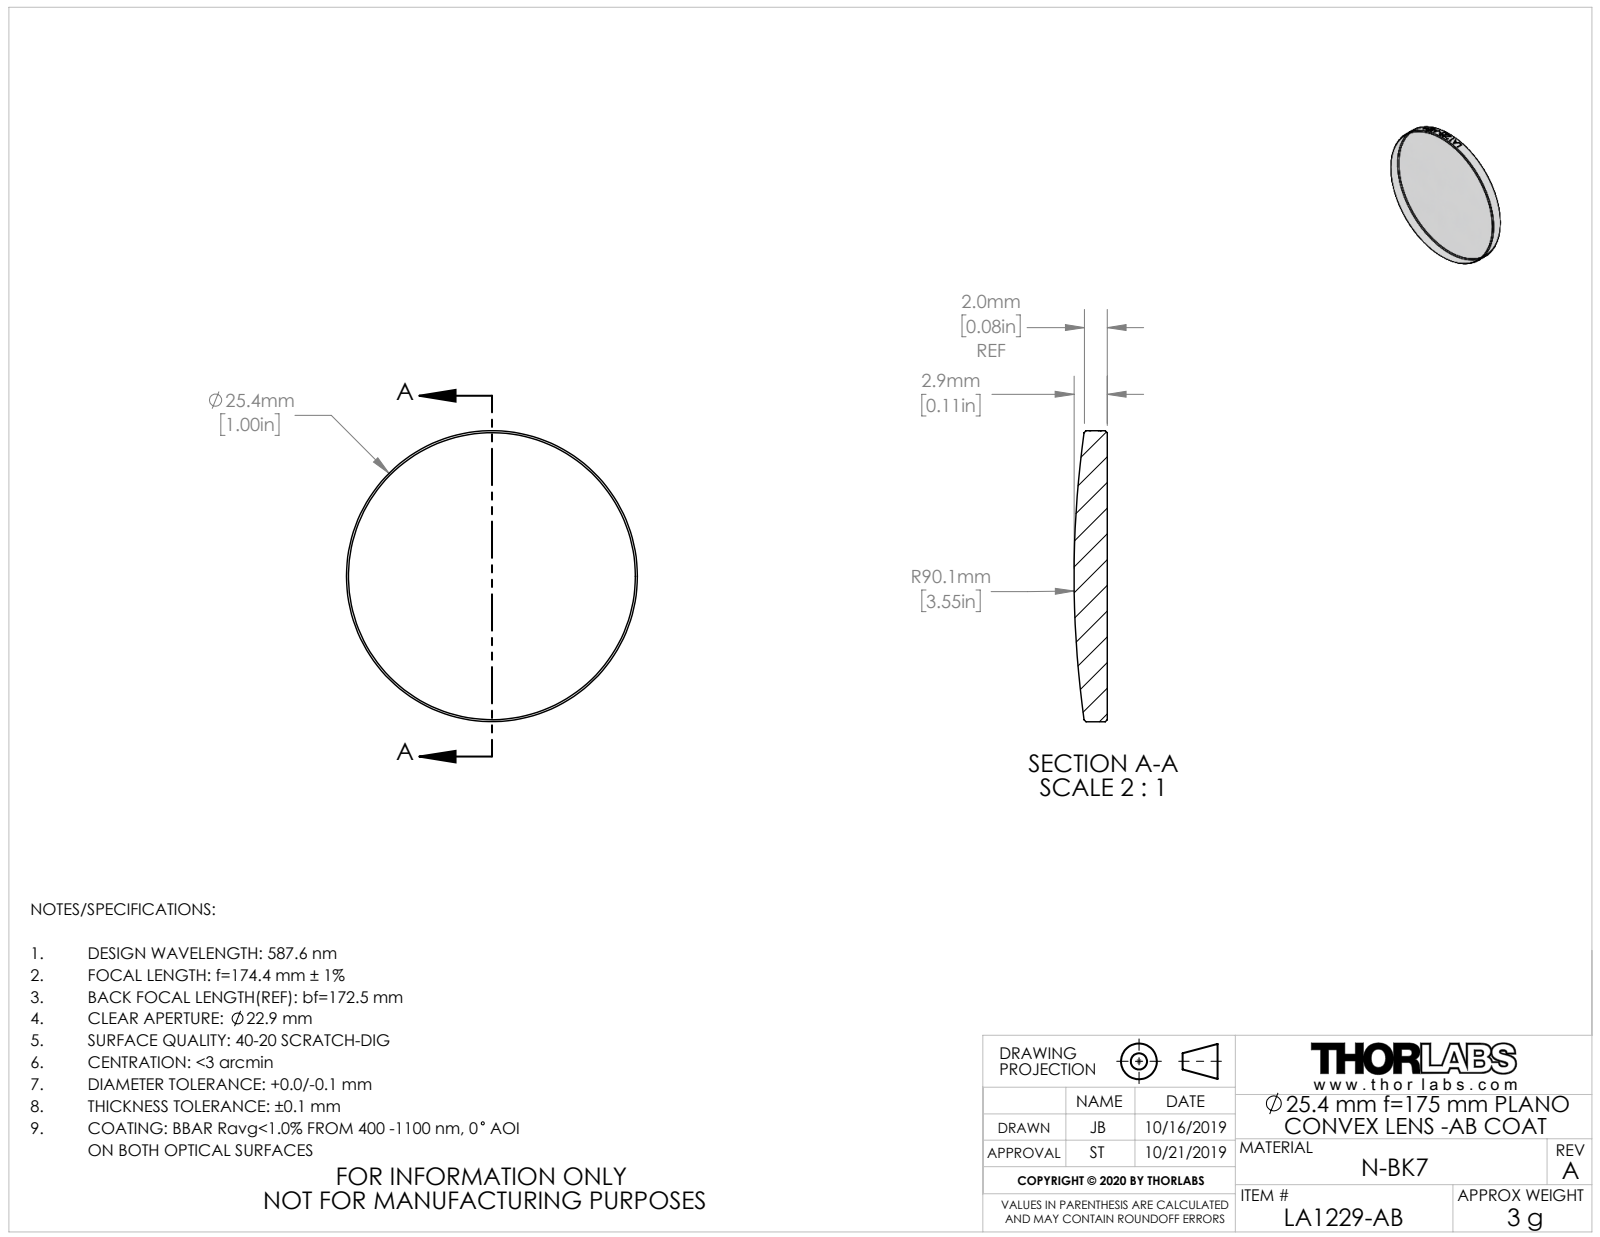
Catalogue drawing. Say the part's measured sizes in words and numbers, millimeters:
The part is named "TTN195774-E0W". Its 3-D file was written by "SolidWorks 2018 (CONFIG_CONTROL_DESIGN)". It is 1 solid with 27 faces: 1 planar, 20 cylindrical and 6 other. Overall it measures 25.4 by 25.4 by 2.9 millimeters. Its volume is 1 200 cubic millimeters and its surface area 1 160 square millimeters. Round bosses or shafts: 1 of diameter 25.4.
